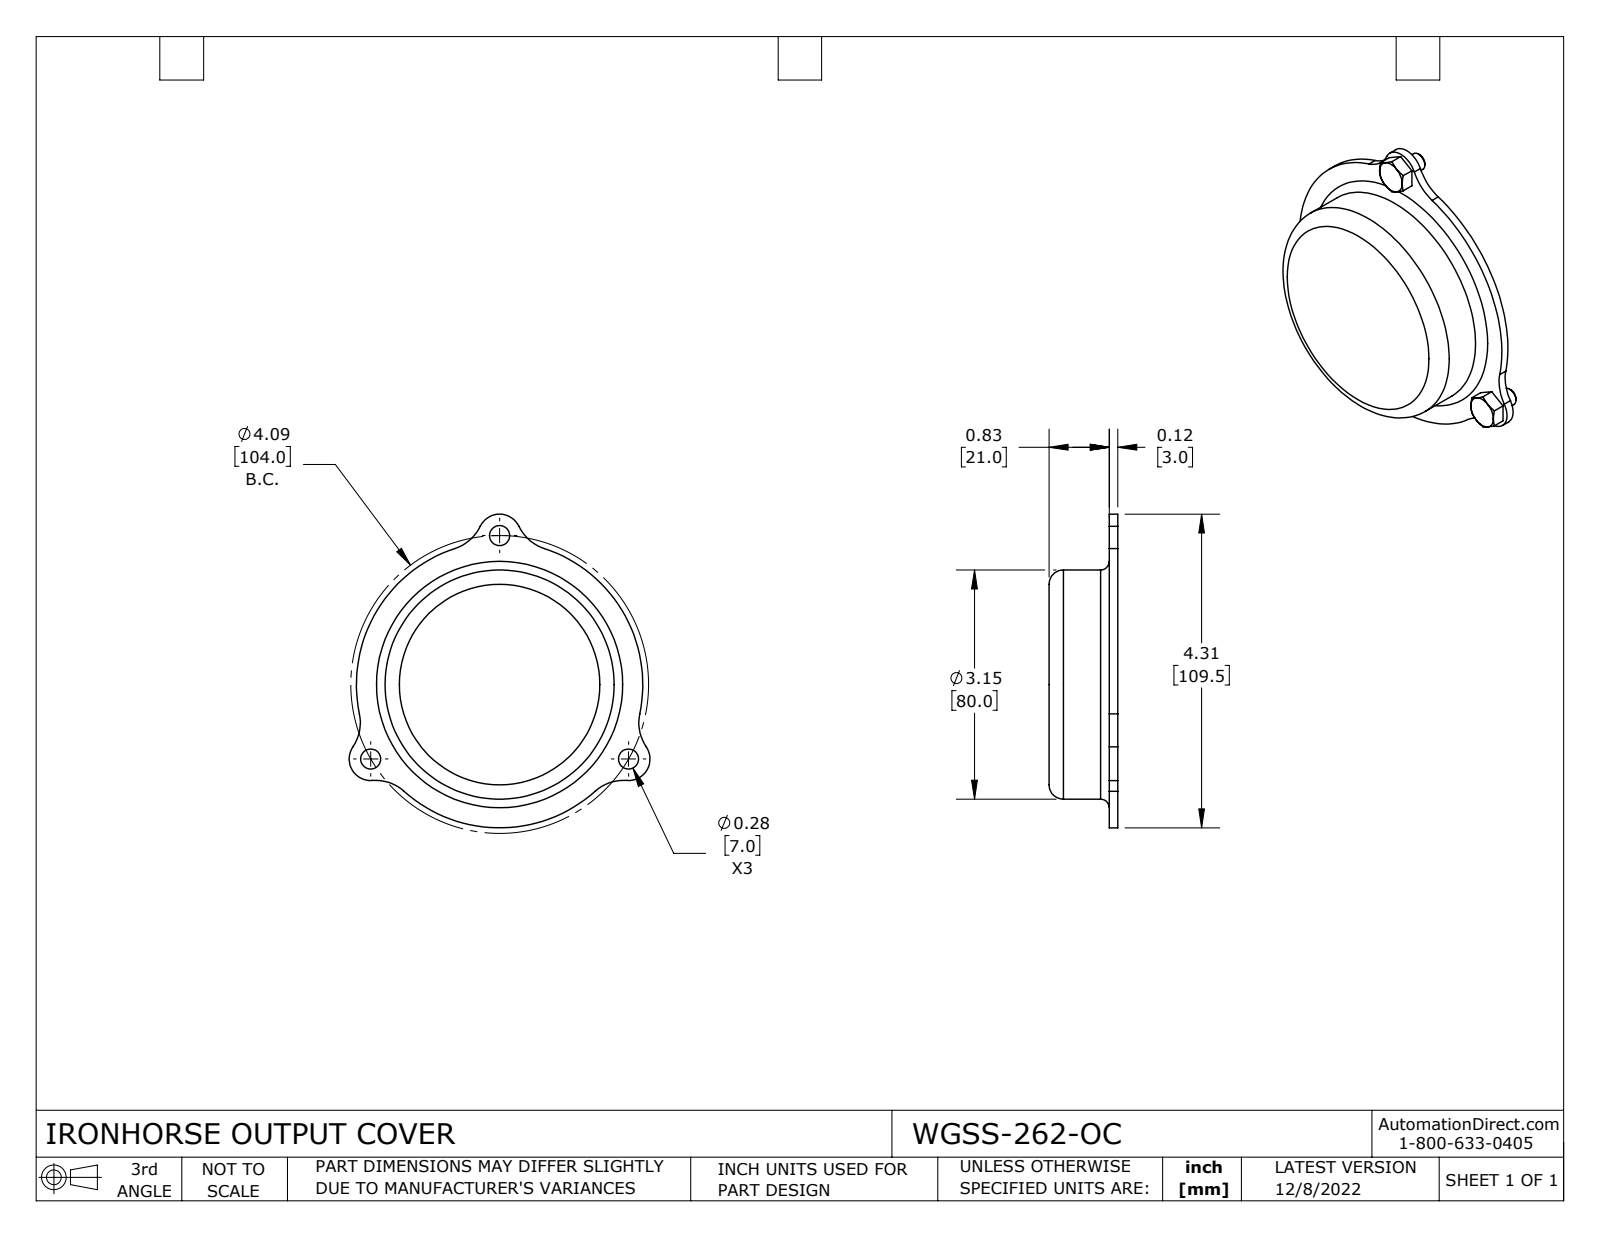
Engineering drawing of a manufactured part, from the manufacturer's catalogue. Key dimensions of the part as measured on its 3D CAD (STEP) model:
Part name (STEP PRODUCT): WGSS-262-OC
STEP written by: SolidWorks 2021 (CONFIG_CONTROL_DESIGN)
Units: inches
Bodies: 4 solids, 94 faces (31 planar, 31 cylindrical, 32 other)
Overall size (bounding box): 4.311 × 4.136 × 1.202
Volume: 1.891 in³ · Surface area: 43.6 in²
Round holes (diameter × count): ⌀0.276 ×3, ⌀2.992 ×1
Round bosses / shafts (diameter × count): ⌀0.25 ×3, ⌀3.15 ×1
Partial cylindrical surfaces — rounded edges, fillets, slot ends (radius × count): R0.591 ×6, R0.295 ×3, R1.969 ×1
Main face-to-face distances: 0.079, 0.748, 0.827, 0.118, 0.866, 0.945, 0.306, 0.188, 0.56, 0.639
Hole centre spacings: 2.047, 3.546
